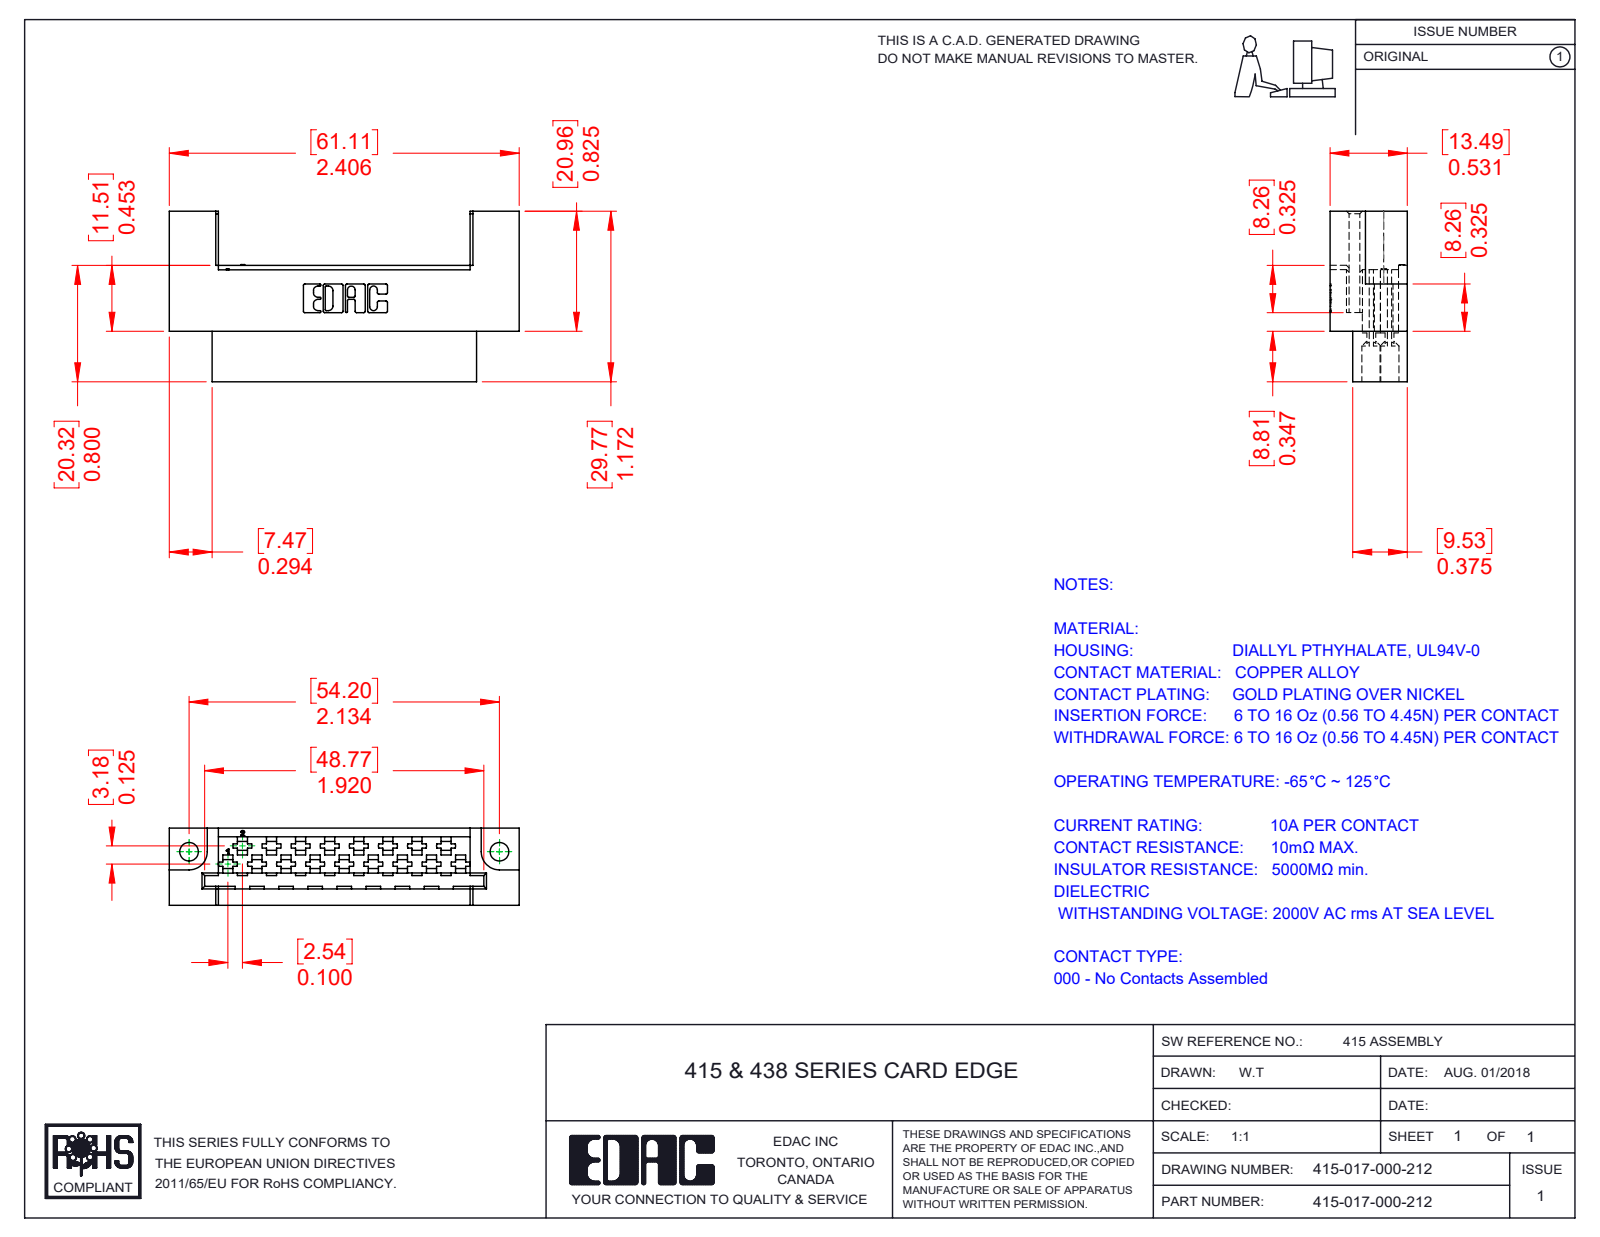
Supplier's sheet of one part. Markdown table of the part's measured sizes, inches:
| quantity | value |
| --- | --- |
| part name | 415-210-001_415-210-017-212; 415-017-000-212 |
| STEP written by | SolidWorks 2016 (CONFIG_CONTROL_DESIGN) |
| units | inches |
| bodies | 1 solid, 602 faces (449 planar, 80 cylindrical, 73 other) |
| overall size | 2.406 × 1.172 × 0.531 |
| volume | 0.642 in³ |
| surface area | 15.04 in² |
| round holes (diameter × count) | 0.13 × 17, 0.128 × 2 |
| partial cylindrical surfaces (radius × count) | 0.01 × 22, 0.007 × 6, 0.031 × 6, 0.026 × 3, 0.125 × 2 |
| main face-to-face distances | 0.531, 0.375, 0.156, 0.125, 0.048, 0.047, 0.029, 0.076, 0.018, 0.124 |
| hole center spacings | 0.16, 0.2, 0.325, 0.4, 0.515, 0.6, 0.711, 0.8 |
